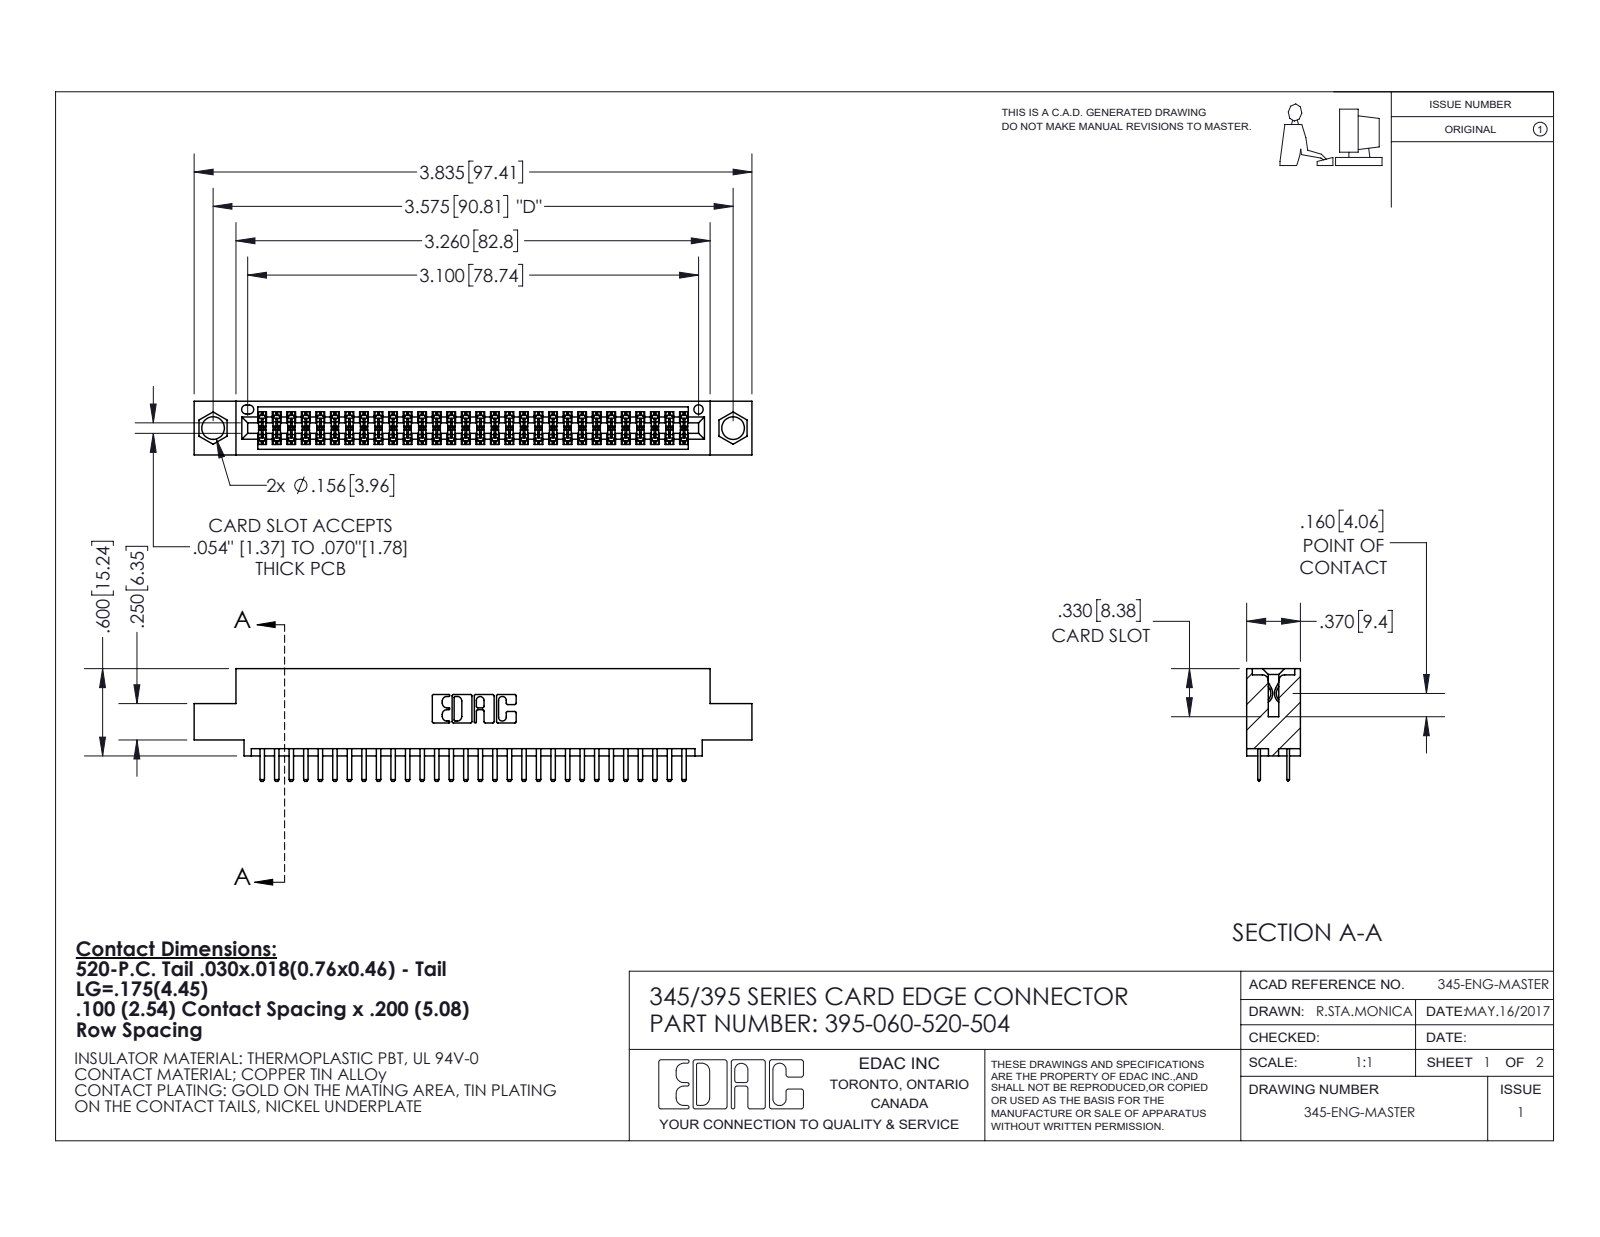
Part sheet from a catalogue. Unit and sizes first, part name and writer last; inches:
Units: inches
Overall size (bounding box): 3.835 × 0.775 × 0.37
Round holes (diameter × count): ⌀0.156 ×2, ⌀0.064 ×1
Partial cylindrical surfaces — rounded edges, fillets, slot ends (radius × count): R0.006 ×120, R0.01 ×64, R0.01 ×22, R0.007 ×6, R0.031 ×6, R0.026 ×3, R0.014 ×2, R0.019 ×2
Main face-to-face distances: 0.072, 0.298, 0.2, 0.37, 0.098, 0.272, 0.025, 0.225, 0.022, 0.072
Hole centre spacings: 0.27, 3.34, 3.575
Volume: 0.558 in³ · Surface area: 20.42 in²
Bodies: 61 solids, 3384 faces (2198 planar, 1186 cylindrical, 0 other)
Part name (STEP PRODUCT): 395-060-520-504; 345 Part_0.110 Offset - 0.156 Dia-TI; 345-292-001_345-293-120
STEP written by: SolidWorks 2020 (CONFIG_CONTROL_DESIGN)
